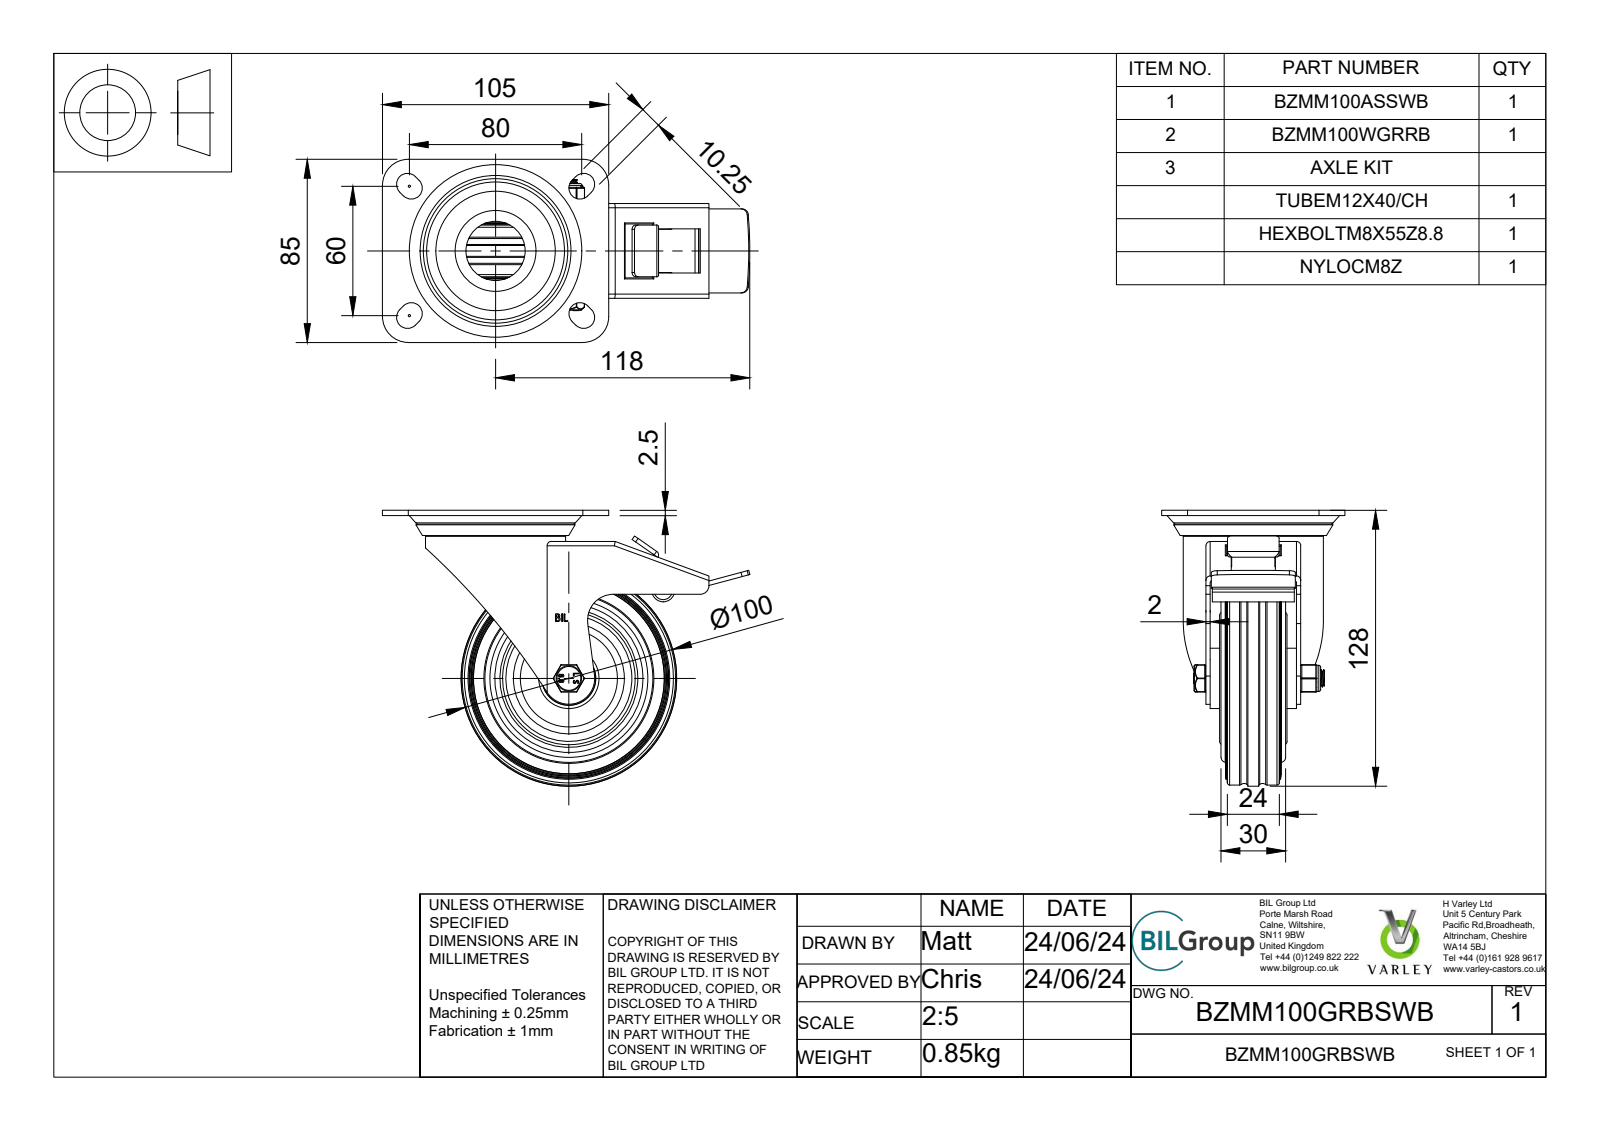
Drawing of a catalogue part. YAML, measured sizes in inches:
part_name: "BZMM100GRBSWB v3; BZMM100ASSWB v1; ZINC PLATED, PRESSED STEEL TOP PLATE; ZINC PLATED, PRESSED STEEL TOP PLATE Geometry (+7 more)"
step_written_by: "Autodesk Translation Framework v13.14.0.145 (AUTOMOTIVE_DESIGN)"
units: inches
bodies: {solids: 45, faces: 744, planar: 361, cylindrical: 196, other: 187}
overall_size: [6.713, 5.039, 3.346]
volume: 15.86
surface_area: 200.7
round_holes:
  - {diameter: 0.026, count: 2}
  - {diameter: 0.315, count: 1}
  - {diameter: 0.323, count: 1}
  - {diameter: 0.331, count: 1}
  - {diameter: 0.339, count: 1}
  - {diameter: 0.472, count: 1}
  - {diameter: 0.512, count: 1}
  - {diameter: 0.866, count: 1}
  - {diameter: 0.984, count: 1}
  - {diameter: 1.083, count: 1}
  - {diameter: 2, count: 1}
  - {diameter: 2.205, count: 1}
round_bosses_or_shafts:
  - {diameter: 0.177, count: 8}
  - {diameter: 3.937, count: 1}
  - {diameter: 3.898, count: 1}
  - {diameter: 2.559, count: 1}
  - {diameter: 2.421, count: 1}
  - {diameter: 1.24, count: 1}
  - {diameter: 1.102, count: 1}
  - {diameter: 0.976, count: 1}
partial_cylinders:
  - {radius: 0.02, count: 22}
  - {radius: 0.01, count: 12}
  - {radius: 0.079, count: 9}
  - {radius: 0.202, count: 8}
  - {radius: 0.039, count: 6}
  - {radius: 0.472, count: 5}
  - {radius: 0.013, count: 4}
  - {radius: 0.025, count: 4}
face_to_face_distances: [0.079, 1.654, 0.098, 0.039, 0.118, 1.575, 1.457, 1.284, 0.197, 1.732]
hole_center_spacings: [0.127, 0.098]
